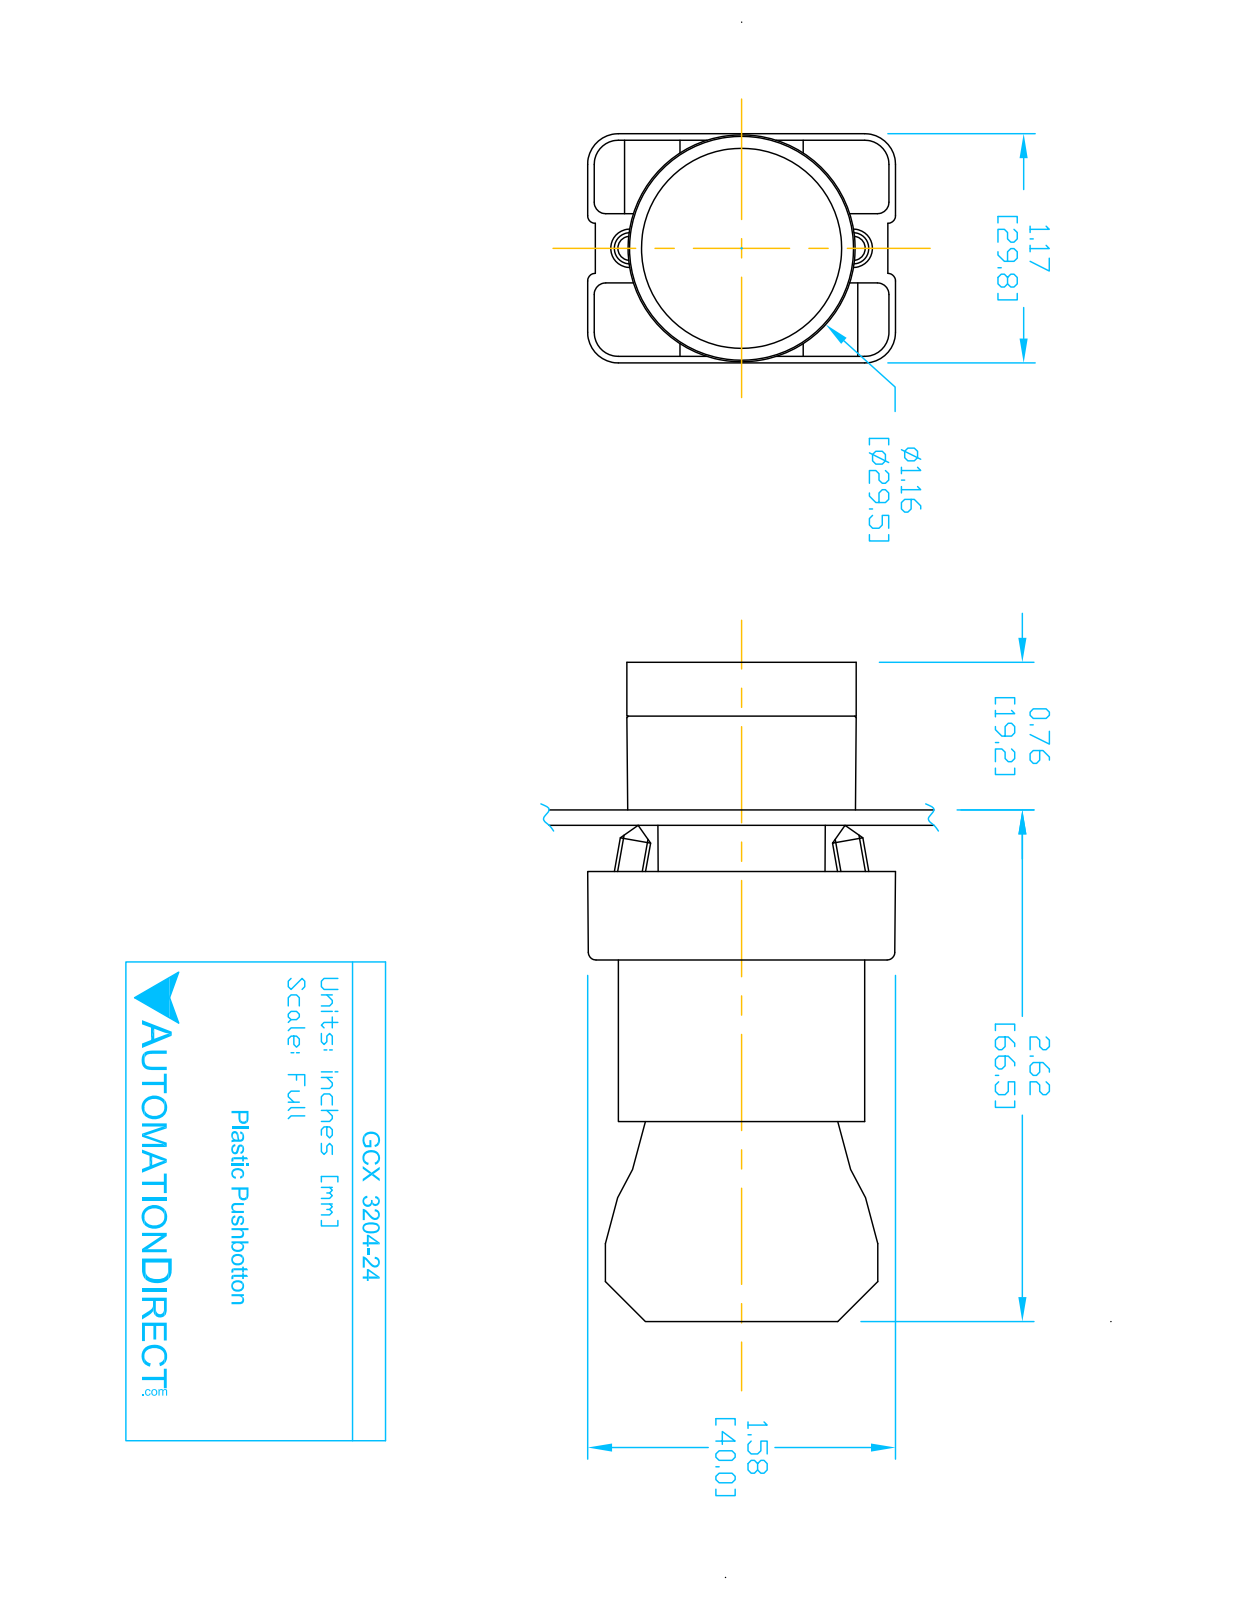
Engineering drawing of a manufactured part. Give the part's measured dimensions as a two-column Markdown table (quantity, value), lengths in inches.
| quantity | value |
| --- | --- |
| part name | ECX3029-2; GCX3204 OPERATOR; ECX1050; GCX3204-24 (+1 more) |
| STEP written by | SolidWorks 2016 (AUTOMOTIVE_DESIGN) |
| units | inches |
| bodies | 8 solids, 431 faces (252 planar, 148 cylindrical, 31 other) |
| overall size | 3.319 × 1.581 × 1.177 |
| volume | 2.794 in³ |
| surface area | 38.77 in² |
| round holes (diameter × count) | 0.079 × 2, 0.124 × 2, 0.13 × 2, 0.087 × 1, 0.197 × 1, 0.469 × 1, 0.878 × 1, 0.888 × 1, 1.024 × 1 |
| round bosses / shafts (diameter × count) | 0.157 × 4, 1.175 × 1, 1.004 × 1, 0.945 × 1, 0.856 × 1, 0.78 × 1, 0.504 × 1 |
| partial cylindrical surfaces (radius × count) | 0.059 × 24, 0.041 × 12, 0.124 × 12, 0.157 × 12, 0.039 × 8, 0.128 × 2, 0.02 × 1, 0.063 × 1 |
| main face-to-face distances | 0.827, 0.579, 2.02, 1.193, 1.171, 0.276, 2.295, 1.469, 0.031, 0.033 |
| hole center spacings | 0.236, 0.544, 0.472, 0.49 |
